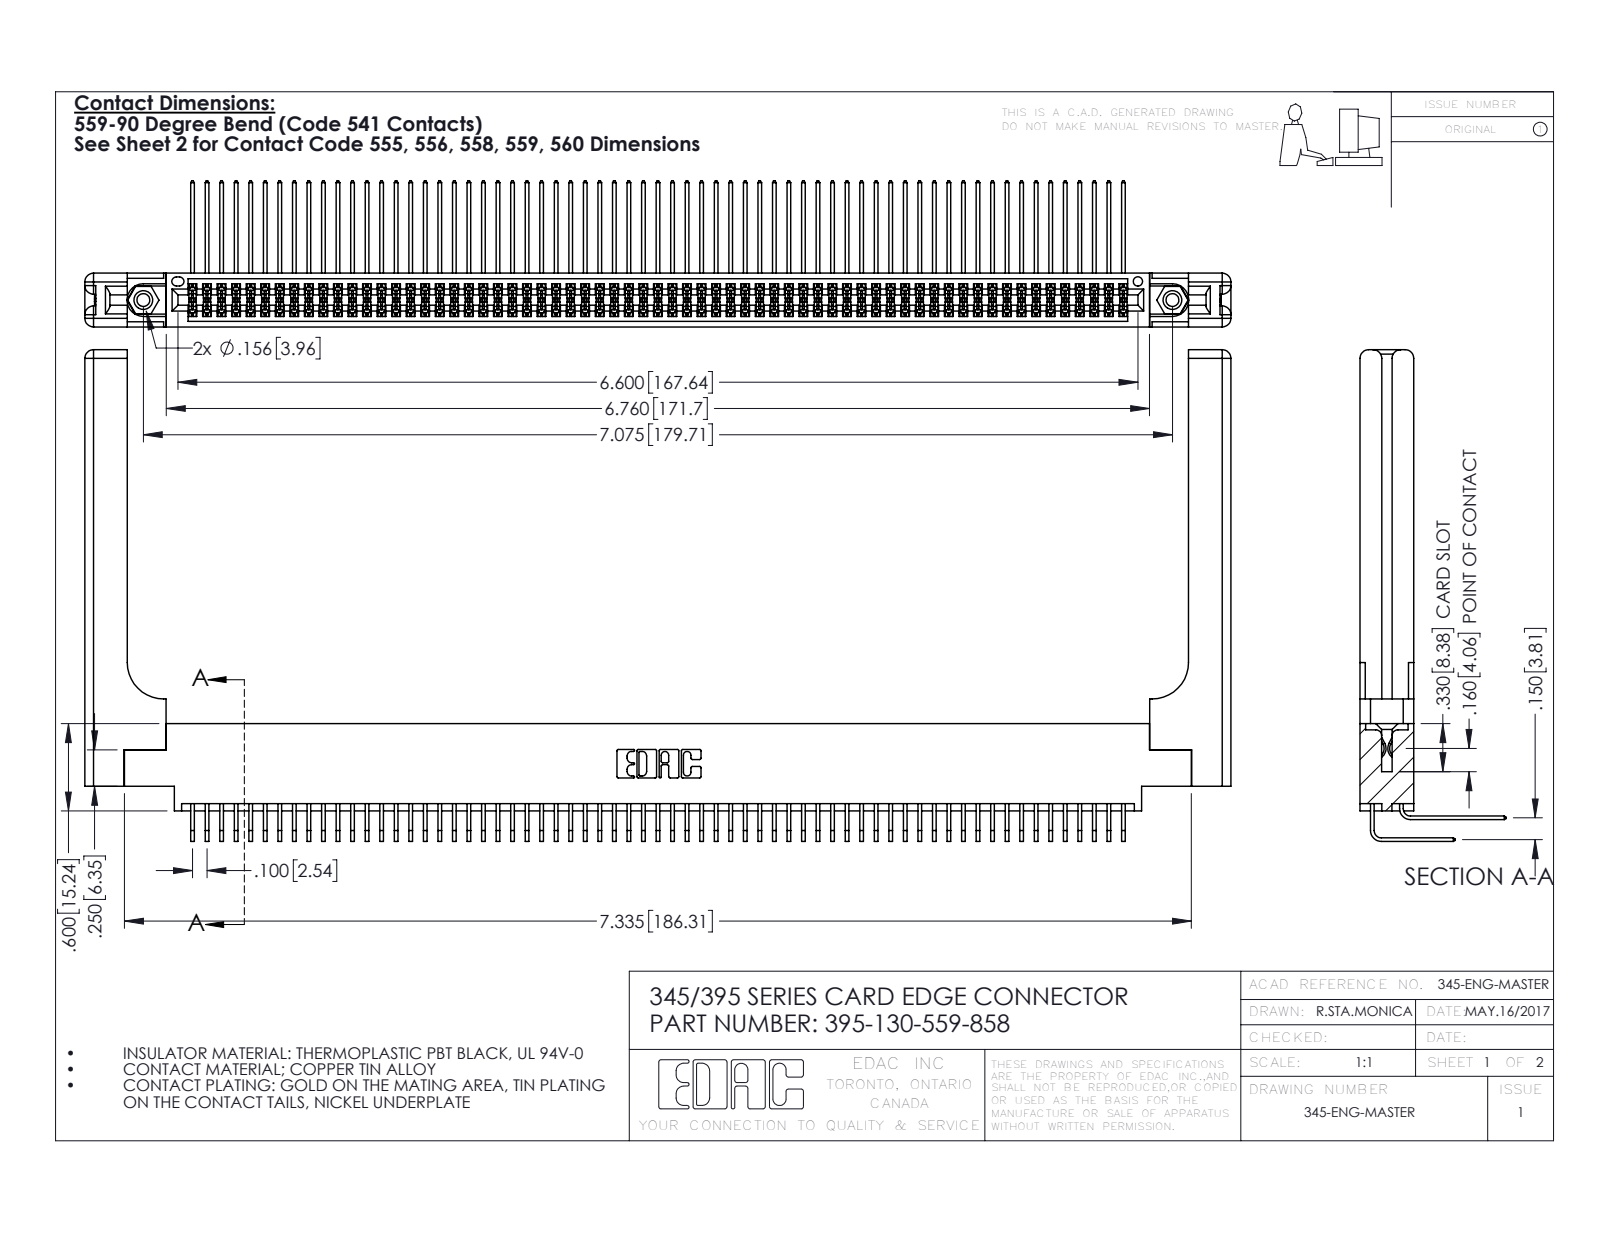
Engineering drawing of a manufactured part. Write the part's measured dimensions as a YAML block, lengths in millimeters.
part_name: "345-292-001_558 559 Tail - 1; 345-292-001_559 Tail - 2; 345-220-058_345-220-058; 345-250-001_345-250-001-102 (+2 more)"
step_written_by: "SolidWorks 2016 (CONFIG_CONTROL_DESIGN)"
units: millimeters
bodies: {solids: 135, faces: 7146, planar: 4782, cylindrical: 2304, other: 60}
overall_size: [200.1, 85.8, 25.5]
volume: 28760
surface_area: 39170
round_holes:
  - {diameter: 2.3, count: 2}
  - {diameter: 3.2, count: 2}
  - {diameter: 4, count: 2}
  - {diameter: 1.6, count: 1}
round_bosses_or_shafts:
  - {diameter: 3.9, count: 2}
partial_cylinders:
  - {radius: 0.2, count: 196}
  - {radius: 0.3, count: 22}
  - {radius: 1.5, count: 16}
  - {radius: 0.2, count: 6}
  - {radius: 0.8, count: 6}
  - {radius: 0.7, count: 3}
  - {radius: 0.4, count: 2}
  - {radius: 0.5, count: 2}
face_to_face_distances: [1.8, 7.6, 9.4, 2.5, 6.9, 0.6, 5.1, 5.7, 4.4, 3.8]
hole_center_spacings: [6.9, 173.7, 179.7]
